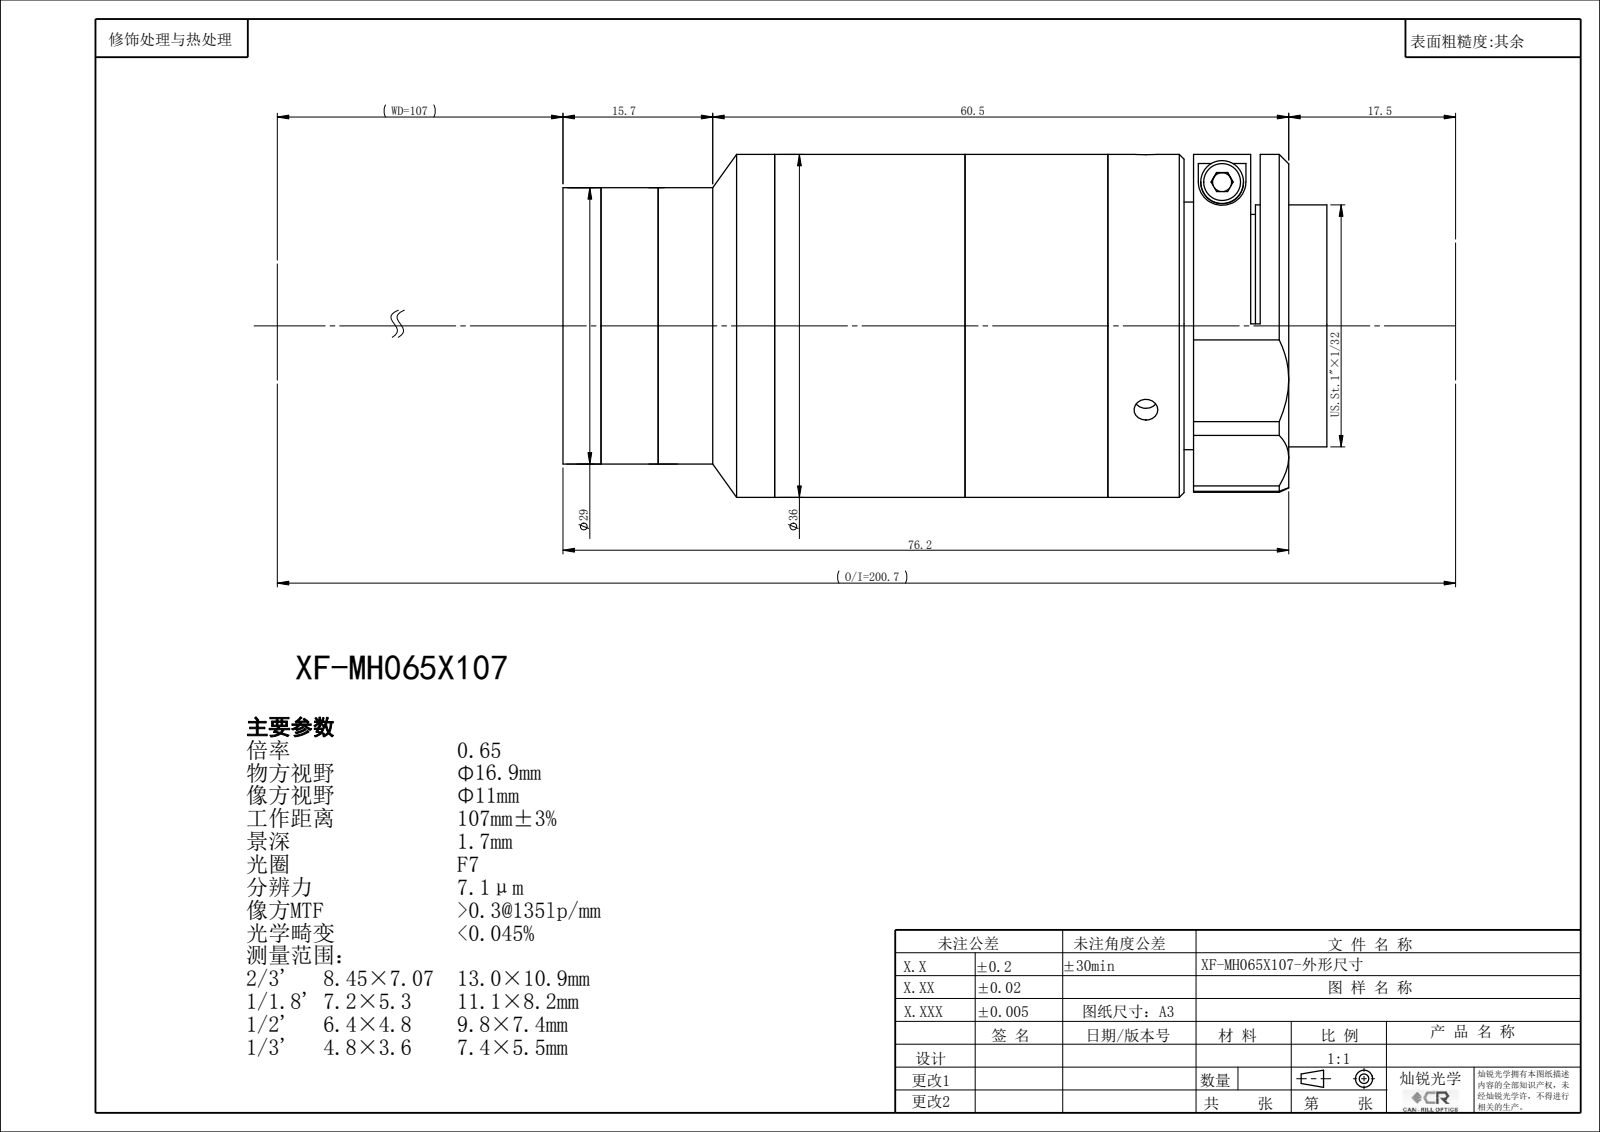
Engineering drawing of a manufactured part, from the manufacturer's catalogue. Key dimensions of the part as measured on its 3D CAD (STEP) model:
Part name (STEP PRODUCT): XF-MH065X107
STEP written by: SolidWorks 2022 (CONFIG_CONTROL_DESIGN)
Units: millimetres
Bodies: 0 solids, 130 faces (66 planar, 42 cylindrical, 22 other)
Overall size (bounding box): 80.2 × 36.01 × 36
Round holes (diameter × count): ⌀2.5 ×3, ⌀14 ×1, ⌀22.4 ×1, ⌀24 ×1, ⌀24.9 ×1, ⌀26 ×1, ⌀26.4 ×1
Round bosses / shafts (diameter × count): ⌀36 ×1, ⌀34 ×1, ⌀29 ×1, ⌀25.4 ×1
Main face-to-face distances: 18.96, 53.44, 72.4, 1.5, 70.9, 17.46, 38.44, 15, 32.46, 33.96
